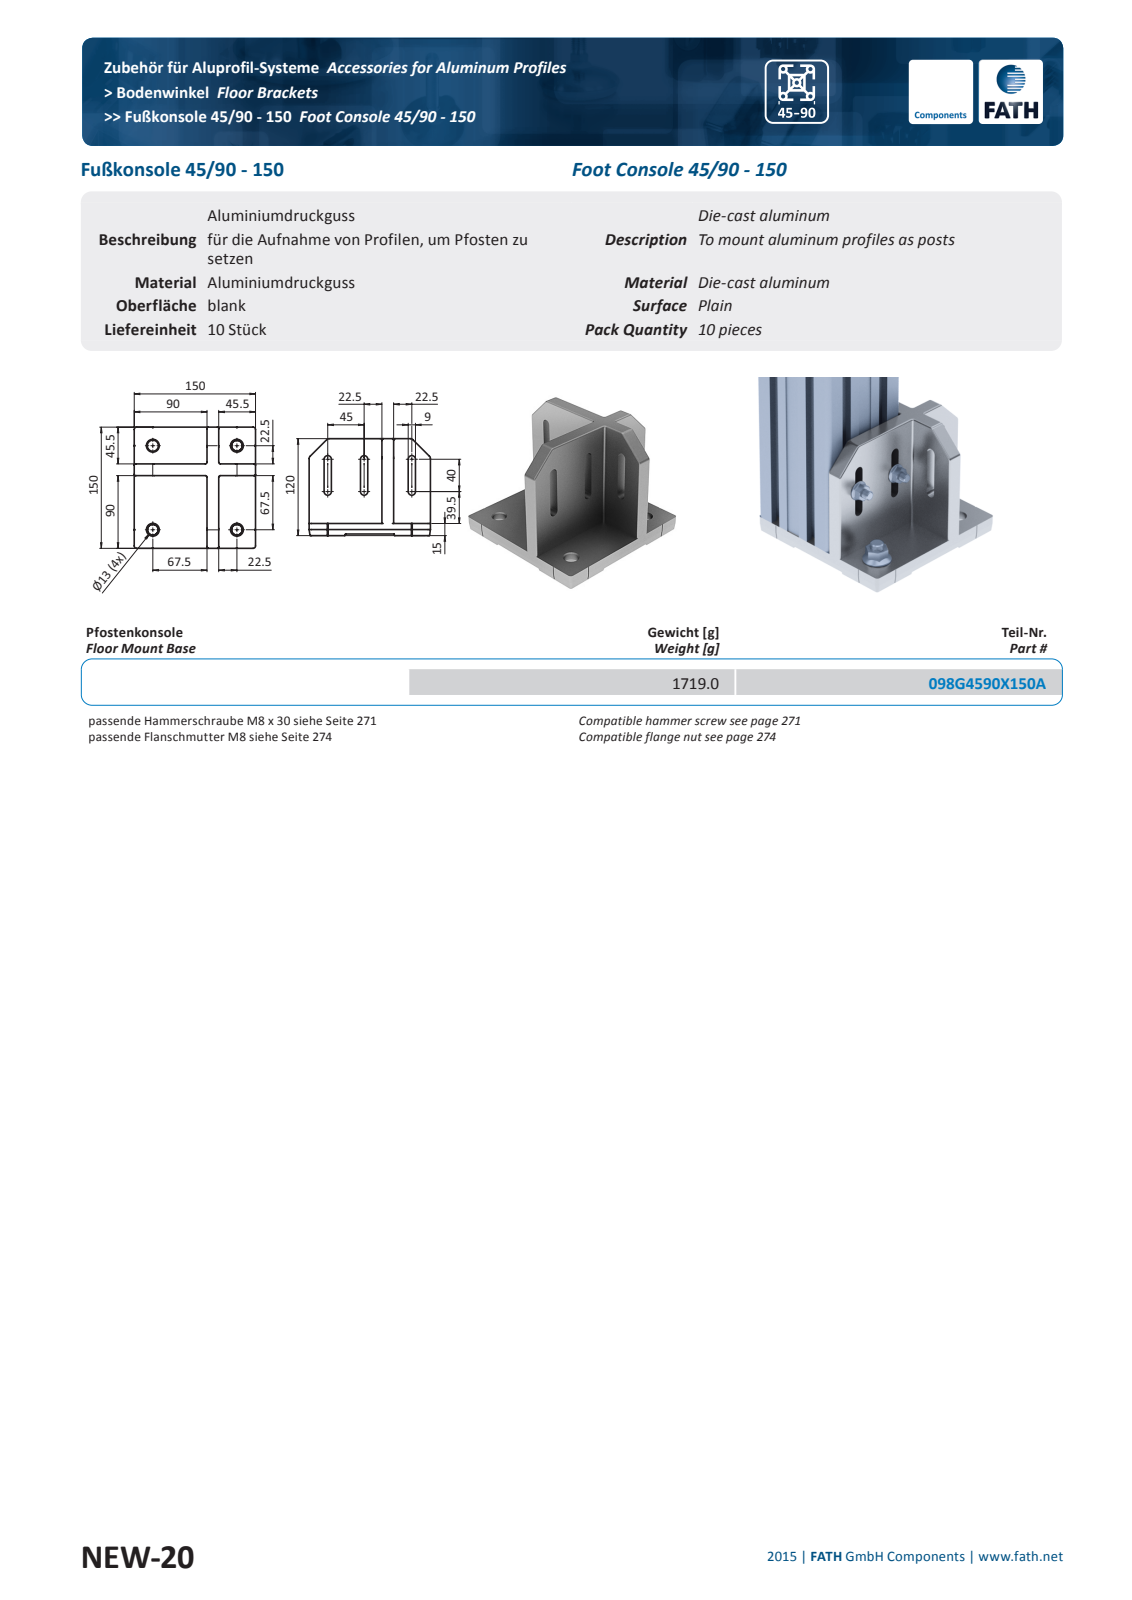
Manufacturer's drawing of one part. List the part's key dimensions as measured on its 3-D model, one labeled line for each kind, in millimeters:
Part name (STEP PRODUCT): fath_098g4590x150a
STEP written by: Spatial InterOp 3D (automotive_design)
Units: millimetres
Bodies: 1 solid, 2252 faces (368 planar, 878 cylindrical, 1006 other)
Overall size (bounding box): 150 × 150 × 120
Volume: 610 196 mm³ · Surface area: 133 870 mm²
Partial cylindrical surfaces — rounded edges, fillets, slot ends (radius × count): R0.8 ×201, R0.5 ×128, R1.5 ×24, R4 ×10, R4.5 ×10, R2 ×4, R3 ×3, R5 ×1
Main face-to-face distances: 14.5, 7.5, 104.5, 45.5, 60, 19.88, 150, 90, 59.65, 5.5
